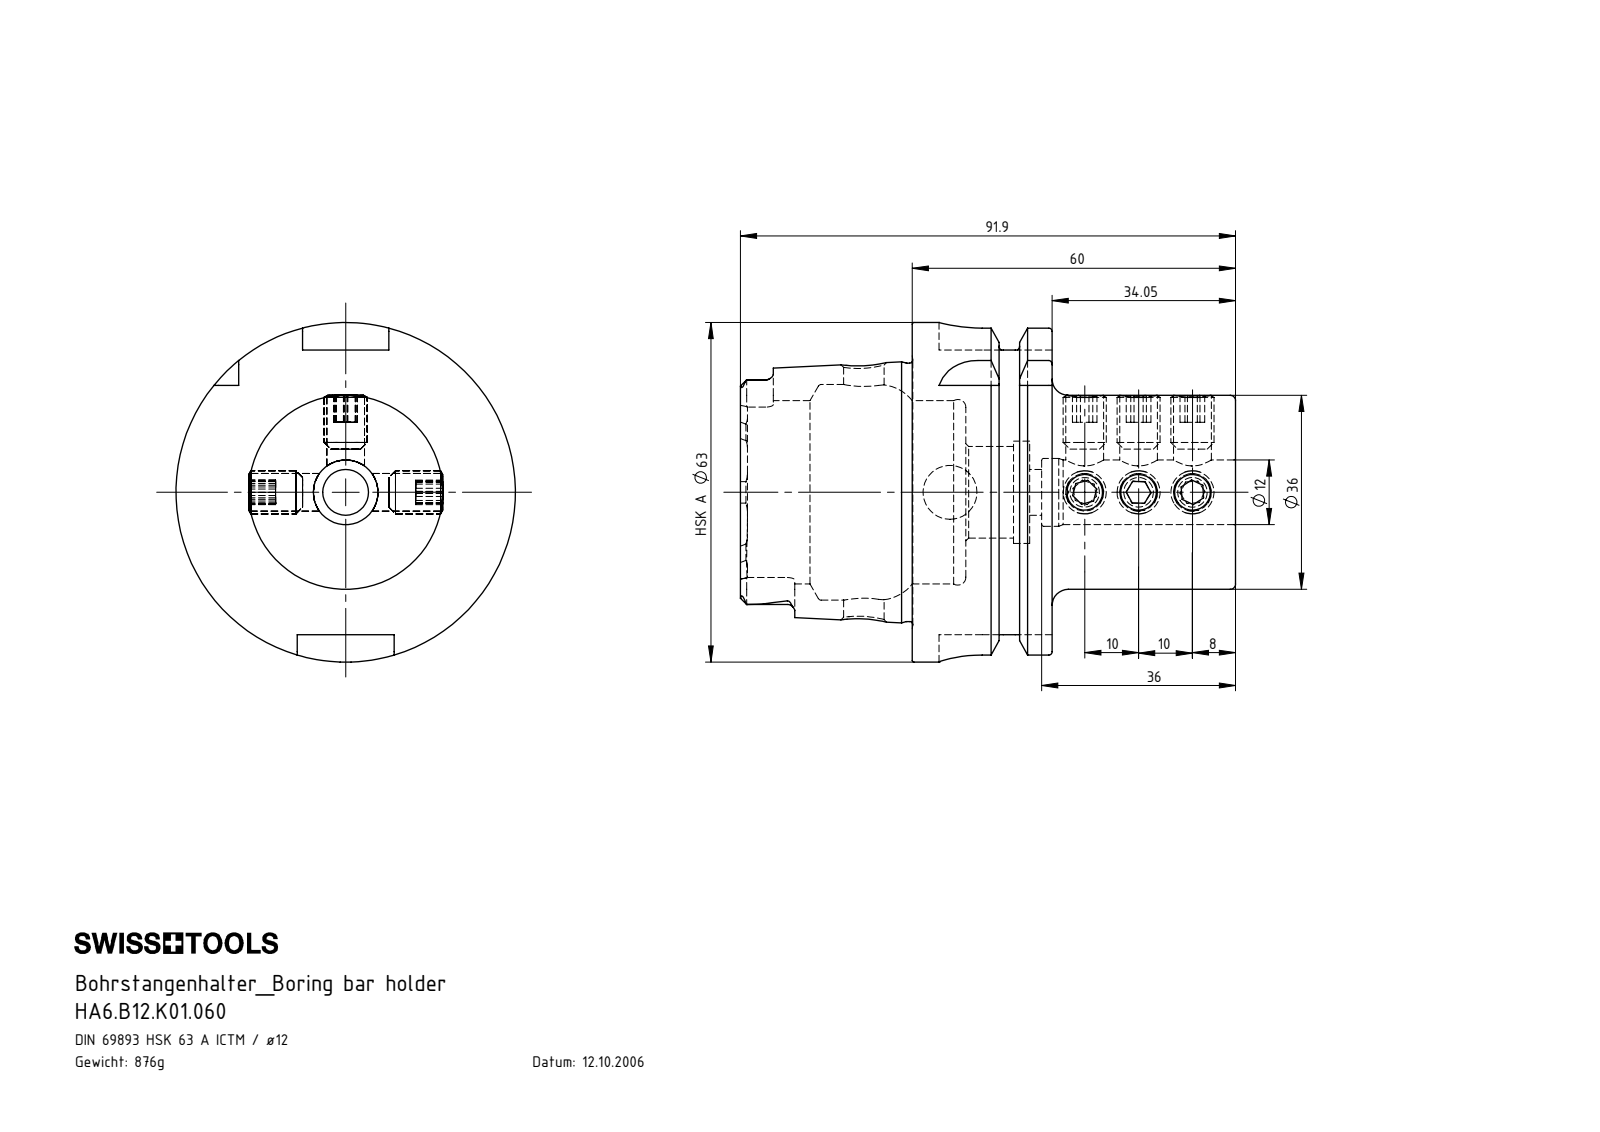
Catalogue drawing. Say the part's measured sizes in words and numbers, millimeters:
The part is named "HA6.B12.K01.060; ISO 4026 - M8 x 10_Default; HA6-B12.K01.060_A_Fertigbearbeitung". Its 3-D file was written by "SolidWorks 2011 (AUTOMOTIVE_DESIGN)". It is 10 solids with 331 faces: 131 planar, 85 cylindrical and 115 other. Overall it measures 91.9 by 63 by 63 millimeters. Its volume is 111 577 cubic millimeters and its surface area 32 465 square millimeters. Round holes: 6 of diameter 7, 1 of diameter 7.5, 1 of diameter 8.5, 1 of diameter 10, 1 of diameter 12, 1 of diameter 12.6, 1 of diameter 17, 1 of diameter 19, 1 of diameter 34, 1 of diameter 40. Round bosses or shafts: 6 of diameter 8, 1 of diameter 63, 1 of diameter 54.95, 1 of diameter 47.94, 1 of diameter 36. Partial cylindrical surfaces (rounded edges, fillets, slot ends): 6 of radius 1.4, 4 of radius 8, 2 of radius 2.88, 1 of radius 2.82, 1 of radius 2.82. The main face-to-face distances are 25.95, 60, 34.05, 16, 9.95, 50.05, 4, 31.9, 41.85, 57.85. The hole center spacings are 10, 20, 25, 35, 41, 45, 51, 61.
